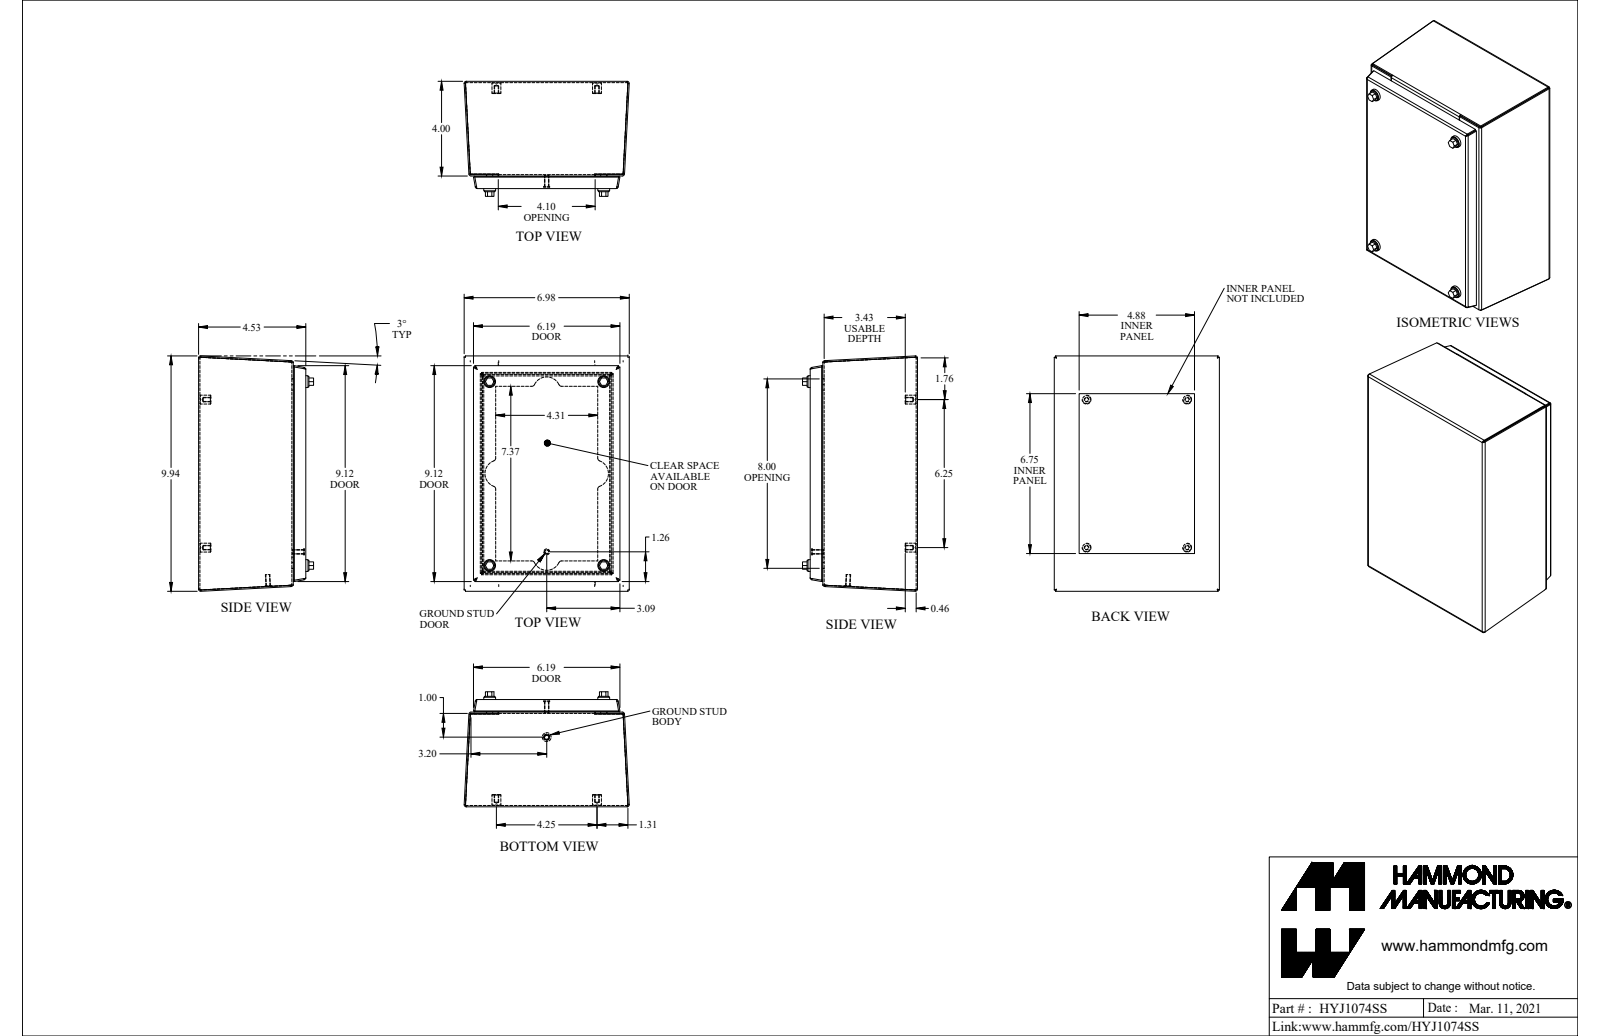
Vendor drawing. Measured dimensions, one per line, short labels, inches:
name: HYJ1074SS
written by: SolidWorks 2021 (AUTOMOTIVE_DESIGN)
unit: in
bodies: 26 solids, 477 faces (305 planar, 140 cylindrical, 32 other)
size: 9.942 × 6.976 × 4.859
volume: 21.87 in³; area: 702.7 in²
holes: 4× ⌀0.065, 4× ⌀0.156, 4× ⌀0.235, 4× ⌀0.239, 4× ⌀0.24, 4× ⌀0.25, 4× ⌀0.253, 4× ⌀0.4
bosses: 8× ⌀0.375, 6× ⌀0.19, 4× ⌀0.5, 4× ⌀0.45, 4× ⌀0.406, 4× ⌀0.315, 2× ⌀0.25
rounds: 16× R0.029, 16× R0.086, 12× R0.125, 4× R0.055, 4× R0.076, 4× R0.5, 4× R0.575
face distances: 0.057, 4.418, 4.475, 0.057, 4.532, 4.475, 3.943, 0.475, 4, 0.532
hole spacings: 9.139, 7.766, 4.819, 7.766, 0.809, 7.014, 4.597, 4.819
